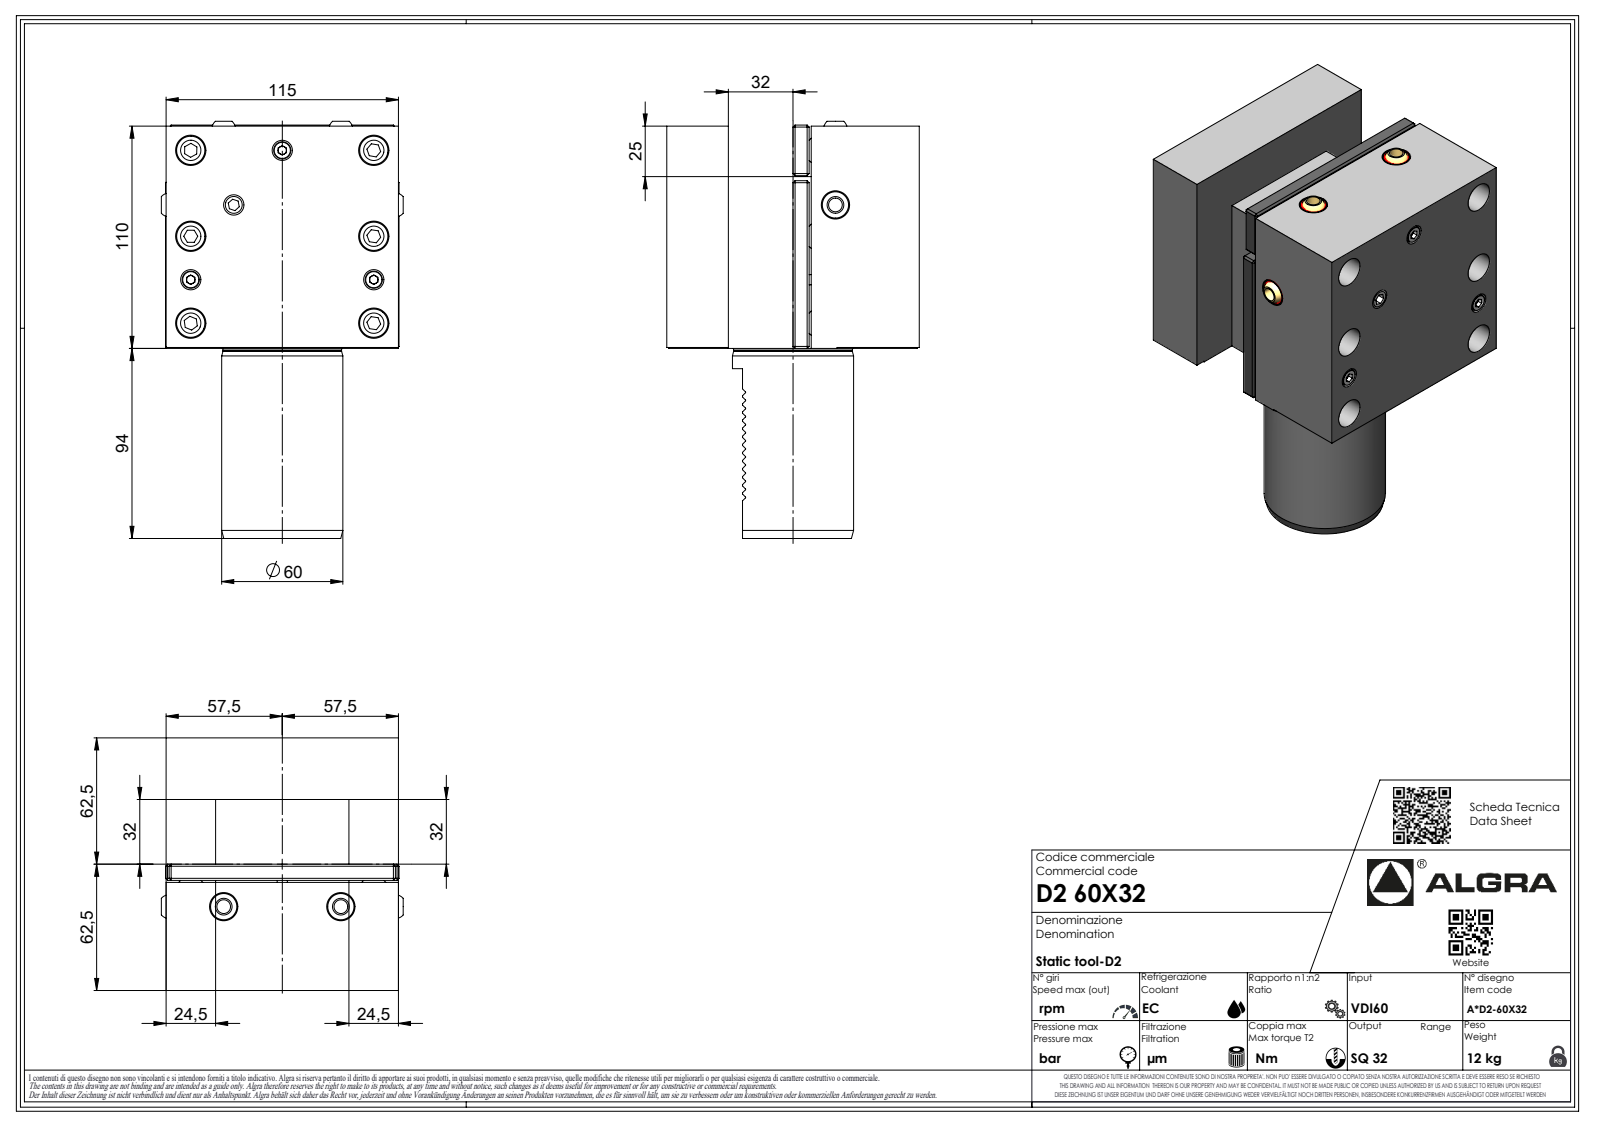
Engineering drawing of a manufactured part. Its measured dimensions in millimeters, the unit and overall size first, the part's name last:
Units: millimetres
Overall size (bounding box): 206.37 × 125 × 119.74
Round holes (diameter × count): ⌀2.1 ×1
Round bosses / shafts (diameter × count): ⌀60 ×1, ⌀58.7 ×1, ⌀6.37 ×1, ⌀1.7 ×1
Partial cylindrical surfaces — rounded edges, fillets, slot ends (radius × count): R0.3 ×14, R0.33 ×7, R0.52 ×7, R3.7 ×7, R0.21 ×1, R61.5 ×1
Main face-to-face distances: 125, 62.5, 94.5, 115, 110, 30.5, 24.5, 32, 90.5, 25
Volume: 1 607 000 mm³ · Surface area: 112 623 mm²
Bodies: 1 solid, 393 faces (284 planar, 44 cylindrical, 65 other)
Part name (STEP PRODUCT): D260X32
STEP written by: SolidWorks 2023 (AUTOMOTIVE_DESIGN)
